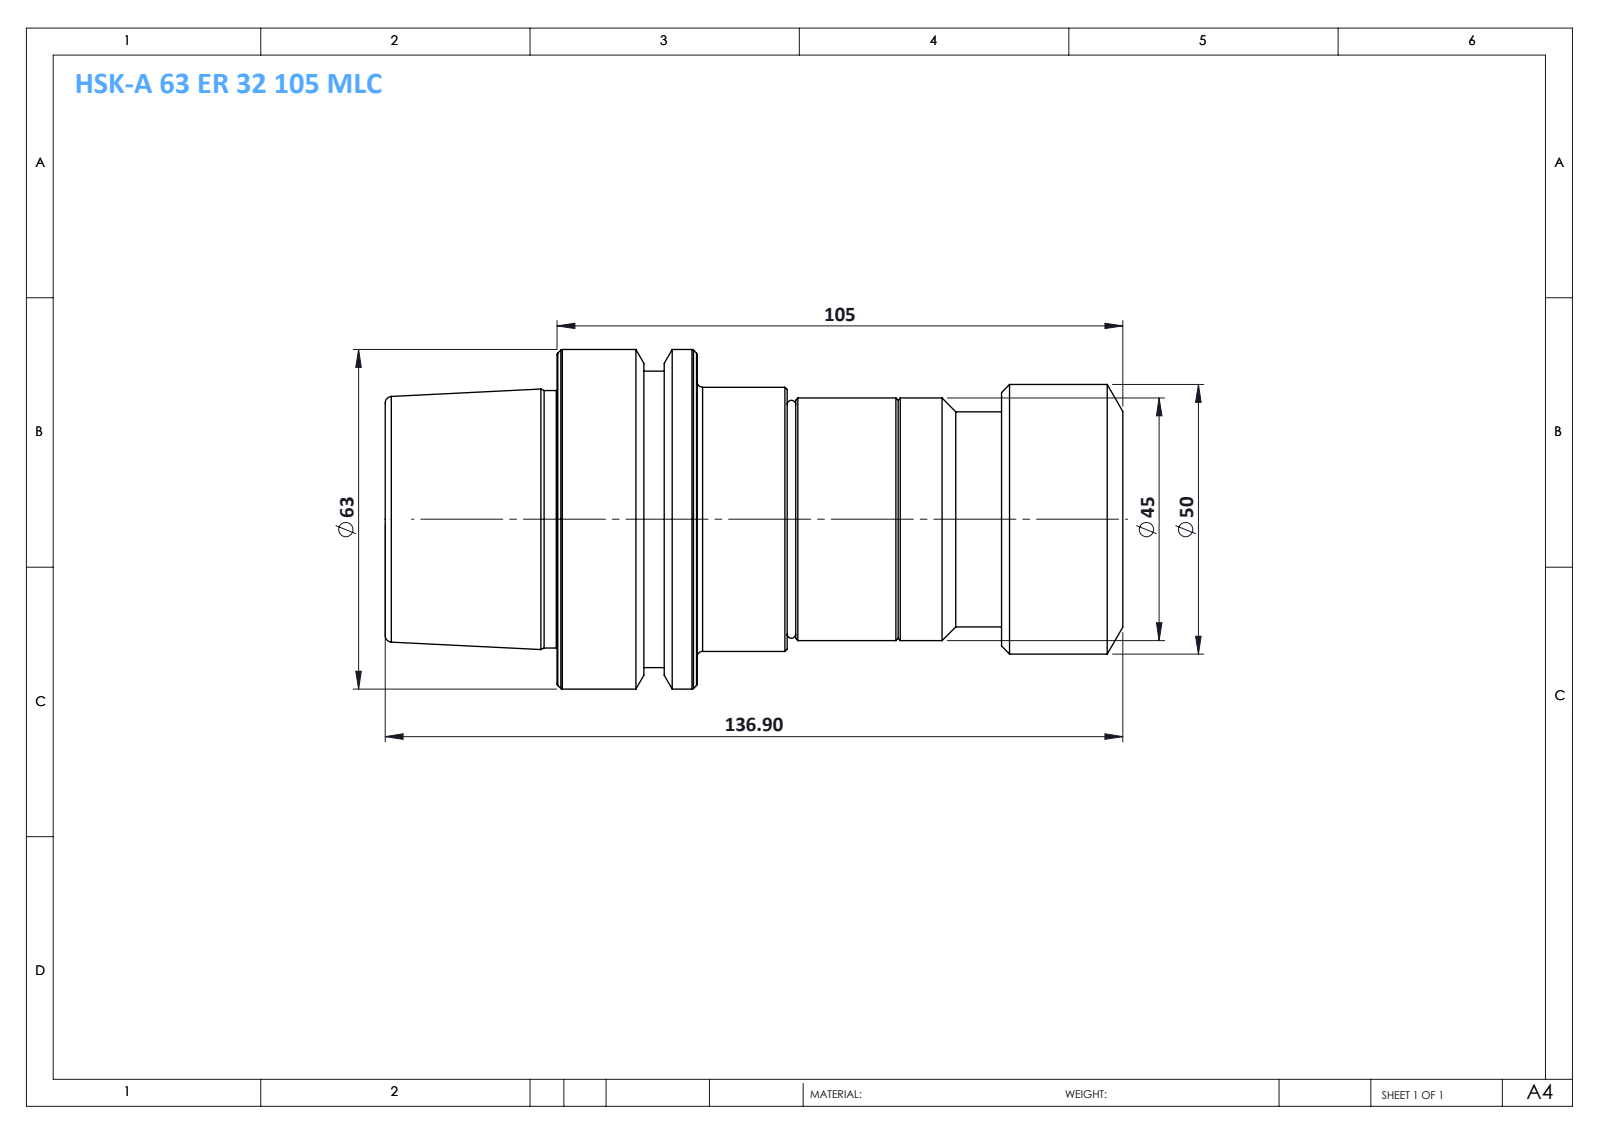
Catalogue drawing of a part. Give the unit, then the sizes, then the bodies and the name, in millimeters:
Units: millimetres
Overall size (bounding box): 136.9 × 63 × 63
Round bosses / shafts (diameter × count): ⌀63 ×1, ⌀55 ×1, ⌀50 ×1, ⌀49 ×1, ⌀47.78 ×1, ⌀45 ×1, ⌀39.9 ×1
Main face-to-face distances: 136.9, 79, 57.9, 105, 26, 31.9, 22.5, 56.5, 82.5, 114.4
Volume: 266 832 mm³ · Surface area: 29 329 mm²
Bodies: 1 solid, 71 faces (9 planar, 18 cylindrical, 44 other)
Part name (STEP PRODUCT): HSK-A 63 ER 32 105 MLC
STEP written by: SolidWorks 2014 (CONFIG_CONTROL_DESIGN)
